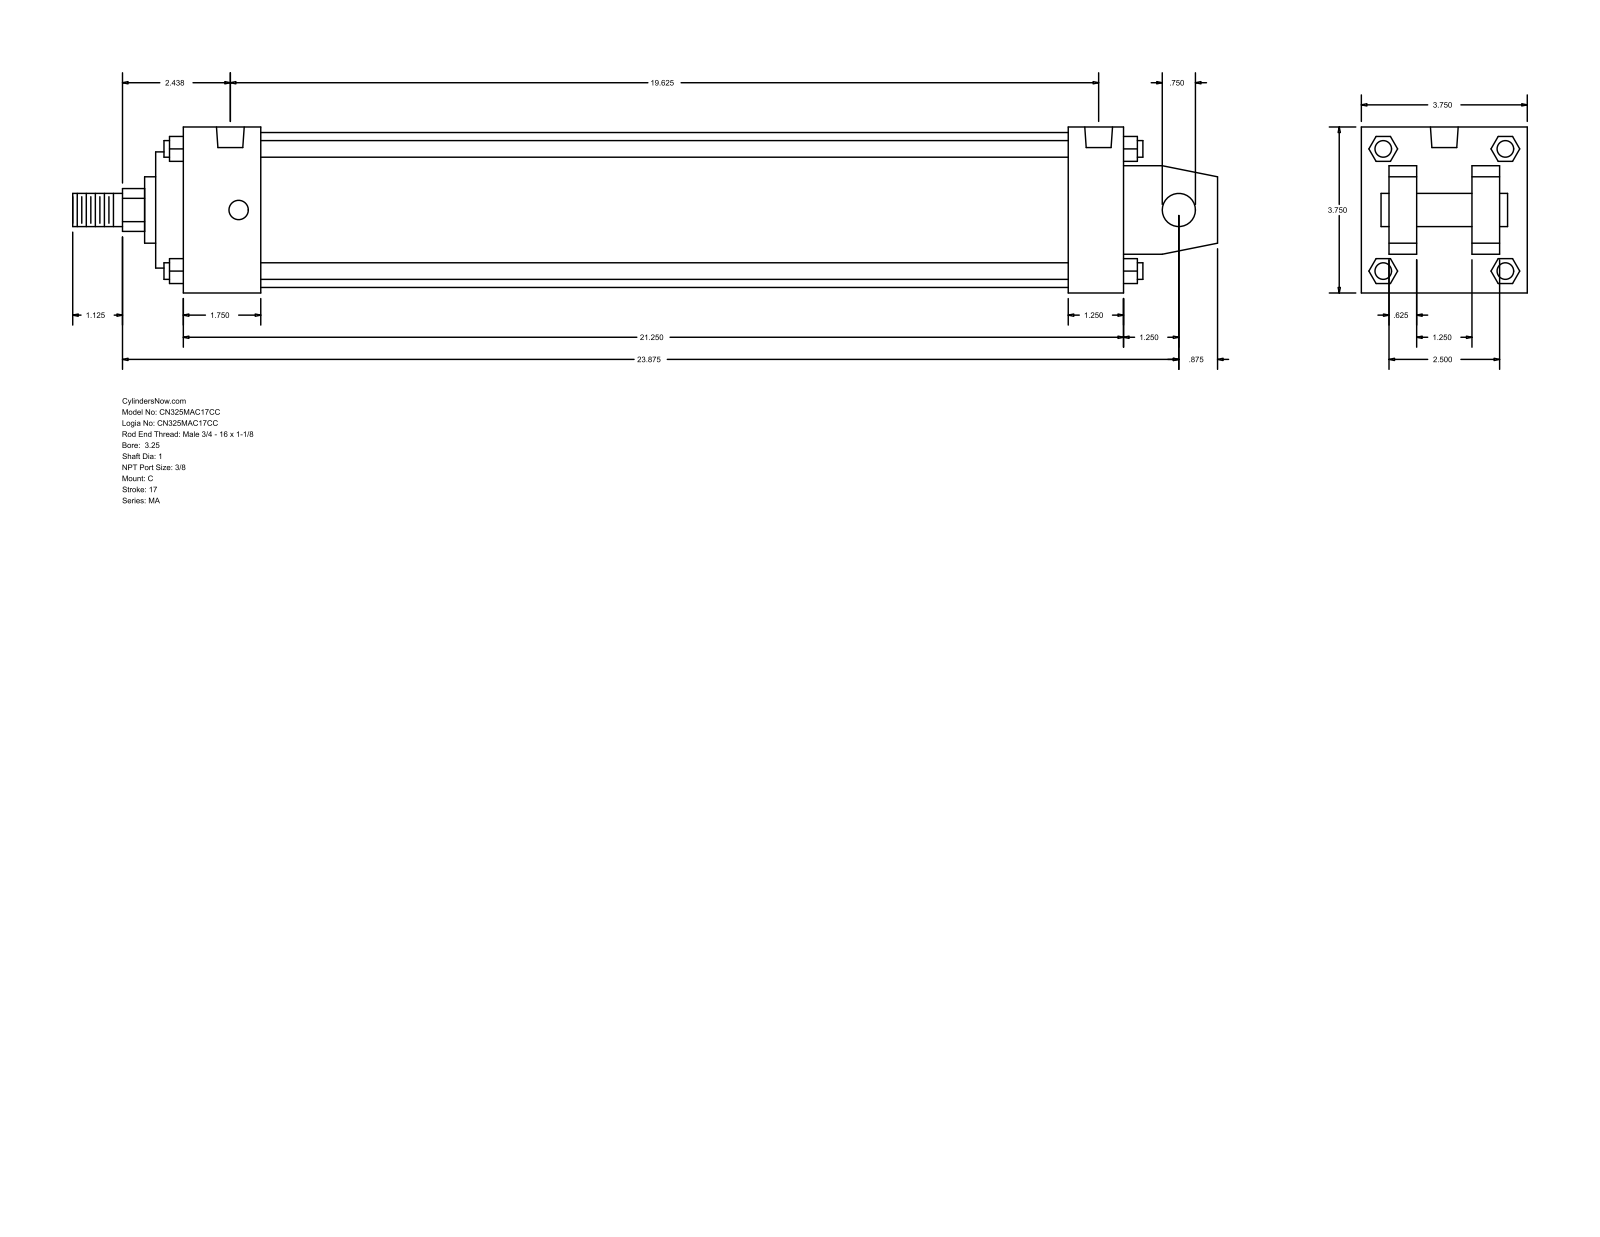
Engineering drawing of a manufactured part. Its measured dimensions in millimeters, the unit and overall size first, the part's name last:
Units: millimetres
Overall size (bounding box): 657.23 × 95.25 × 95.25
Round holes (diameter × count): ⌀11.11 ×4, ⌀15.93 ×2
Round bosses / shafts (diameter × count): ⌀9.53 ×4, ⌀19.05 ×2, ⌀88.9 ×1, ⌀66.67 ×1, ⌀38.1 ×1, ⌀25.4 ×1
Partial cylindrical surfaces — rounded edges, fillets, slot ends (radius × count): R12.29 ×1
Main face-to-face distances: 95.24, 15.87, 63.5, 539.75, 31.74, 79.37, 47.63, 555.62, 508, 31.75
Hole centre spacings: 488.95, 4.76, 4.77, 493.71, 493.72, 498.48
Bodies: 0 solids, 141 faces (109 planar, 32 cylindrical, 0 other)
Part name (STEP PRODUCT): MA_C__0325_1
STEP written by: GSSL Pune (CONFIG_CONTROL_DESIGN)
